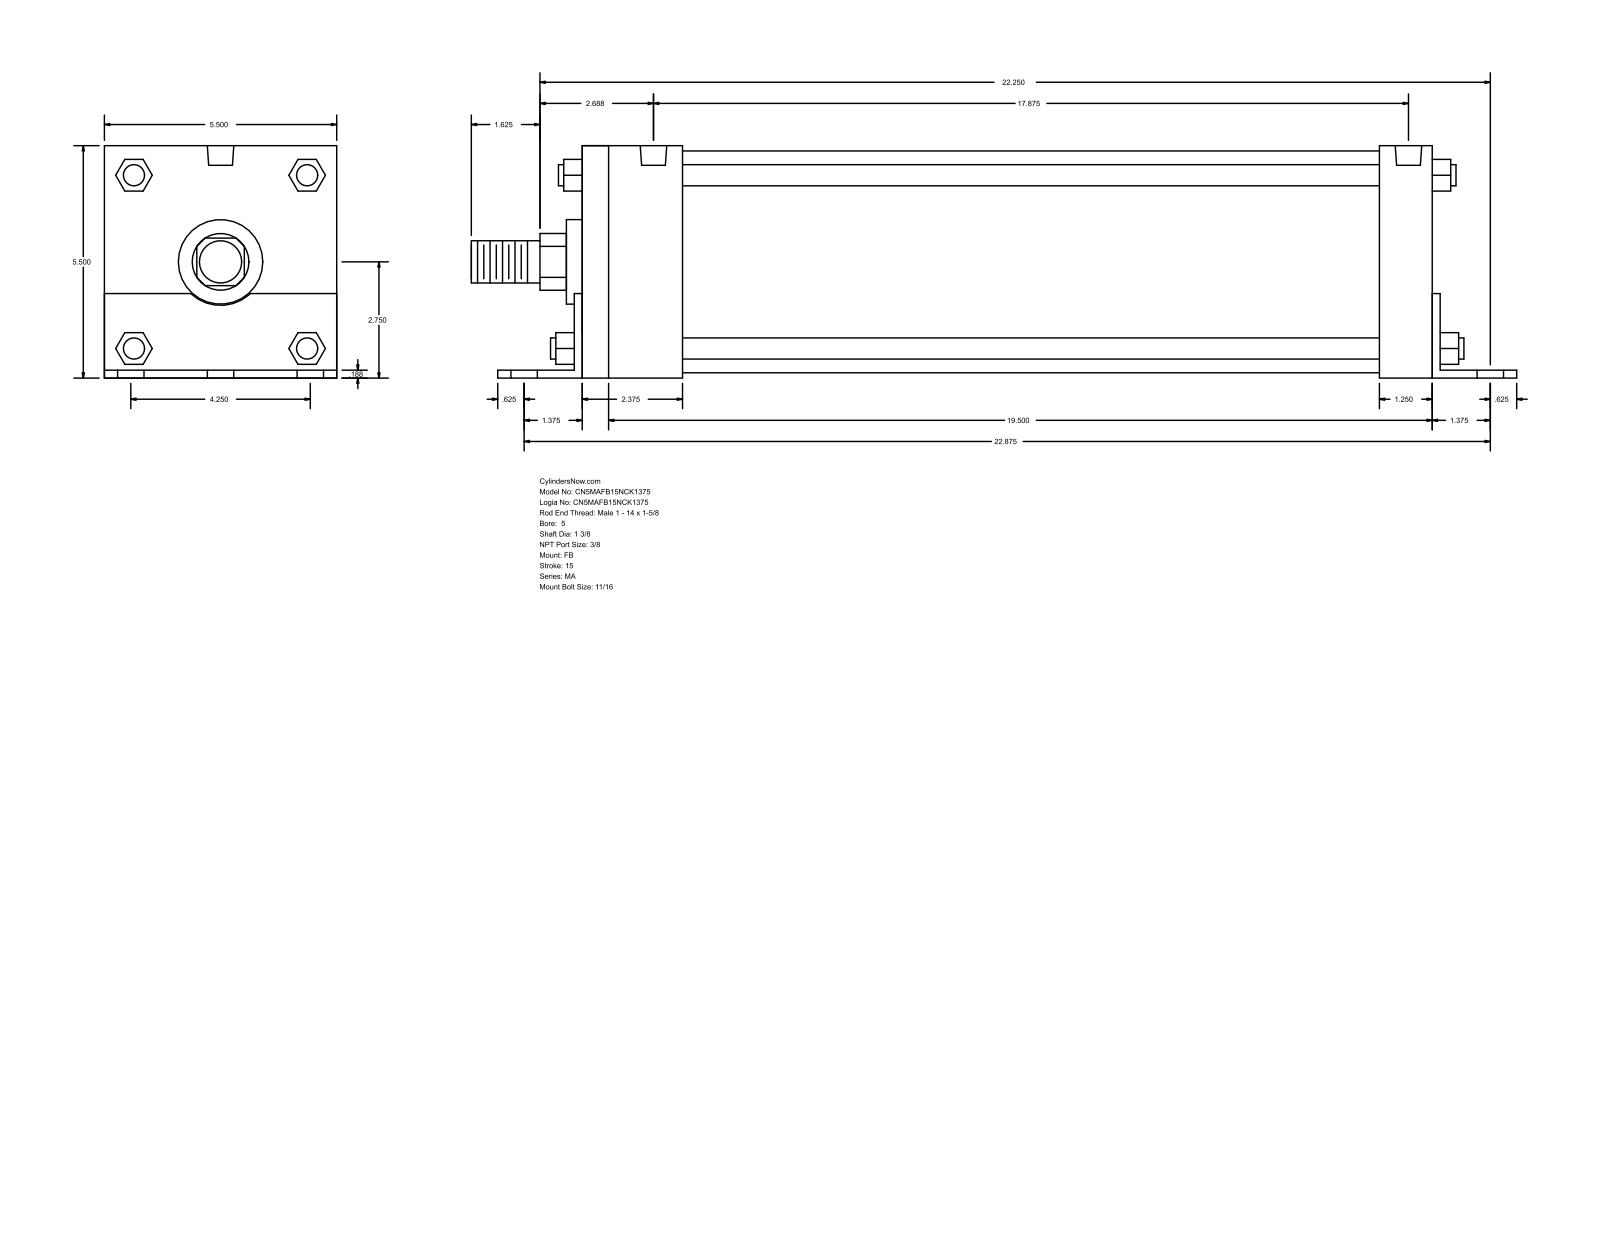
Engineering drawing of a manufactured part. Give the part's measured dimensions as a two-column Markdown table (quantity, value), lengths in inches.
| quantity | value |
| --- | --- |
| part name | MA_FB__0500_1.375 |
| STEP written by | GSSL Pune (CONFIG_CONTROL_DESIGN) |
| units | inches |
| bodies | 0 solids, 140 faces (105 planar, 35 cylindrical, 0 other) |
| overall size | 24.75 × 5.502 × 5.5 |
| round holes (diameter × count) | 0.687 × 6, 0.437 × 4, 0.627 × 2 |
| round bosses / shafts (diameter × count) | 0.5 × 4, 5.25 × 1, 2 × 1, 1.375 × 1, 1 × 1 |
| partial cylindrical surfaces (radius × count) | 0.672 × 1, 1.03 × 1 |
| main face-to-face distances | 5.5, 0.187, 5.502, 20.313, 0.185, 5.315, 20.125, 20.5, 1.25, 1.438 |
| hole center spacings | 2.125, 22.974, 22.875, 0.188, 2.876, 3.006, 3.728, 3.883 |
